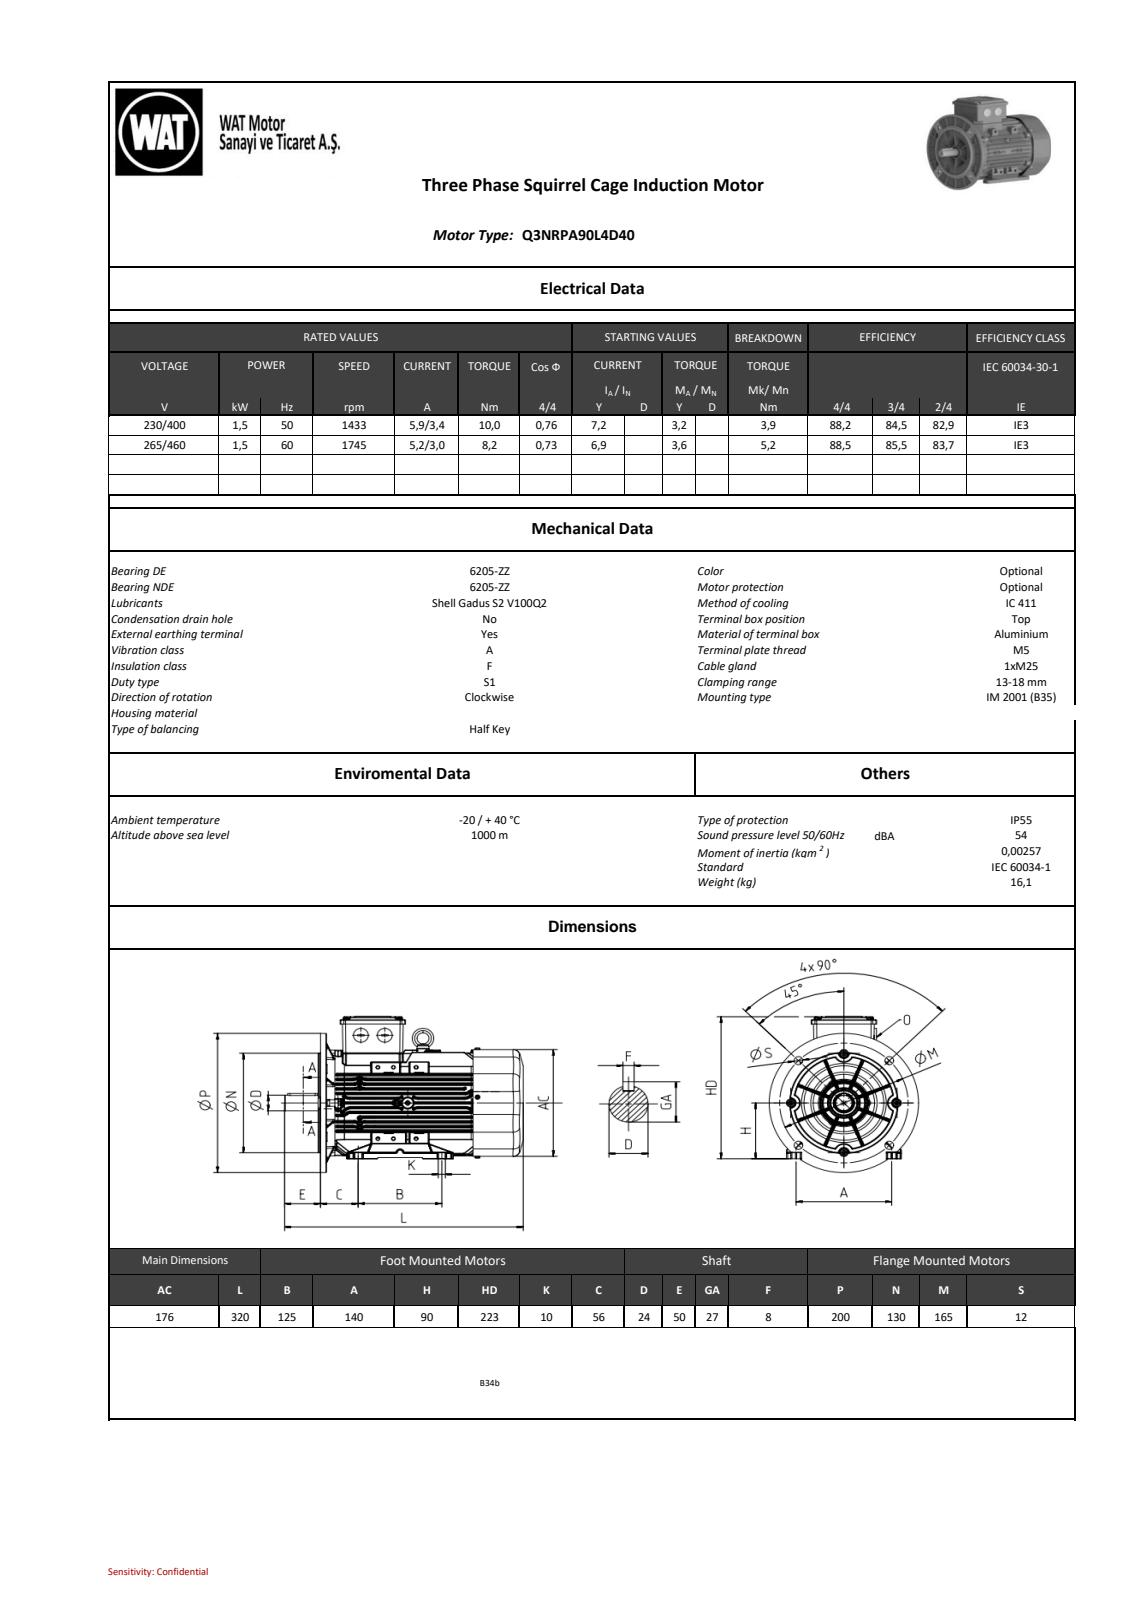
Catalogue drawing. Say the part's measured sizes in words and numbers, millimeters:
The part is named "C9012E981686bajy". Its 3-D file was written by "SIEMENS PLM Software NX 11.0 (AUTOMOTIVE_DESIGN)". It is 0 solids with 15809 faces: 3843 planar, 4972 cylindrical and 6994 other. Overall it measures 320 by 219.47 by 198.95 millimeters. Round holes: 6 of diameter 4.2, 6 of diameter 5.1, 6 of diameter 9, 4 of diameter 12, 2 of diameter 2, 2 of diameter 2.5, 2 of diameter 3, 2 of diameter 7, 1 of diameter 4, 1 of diameter 8, 1 of diameter 12.2, 1 of diameter 23.9. Round bosses or shafts: 12 of diameter 5, 7 of diameter 8, 7 of diameter 4, 6 of diameter 9.4, 6 of diameter 9.2, 6 of diameter 8.5, 3 of diameter 25, 2 of diameter 35. Partial cylindrical surfaces (rounded edges, fillets, slot ends): 1380 of radius 0.5, 671 of radius 1, 503 of radius 0.8, 176 of radius 0.2, 162 of radius 0.3, 131 of radius 1.5, 88 of radius 4, 83 of radius 2. The main face-to-face distances are 4.49, 4.48, 4.5, 4.79, 4.19, 4.78, 56, 4.18, 0.8, 105. The hole center spacings are 20, 81, 14.14, 14.15, 28.28, 92.93, 132.7, 10.09.
